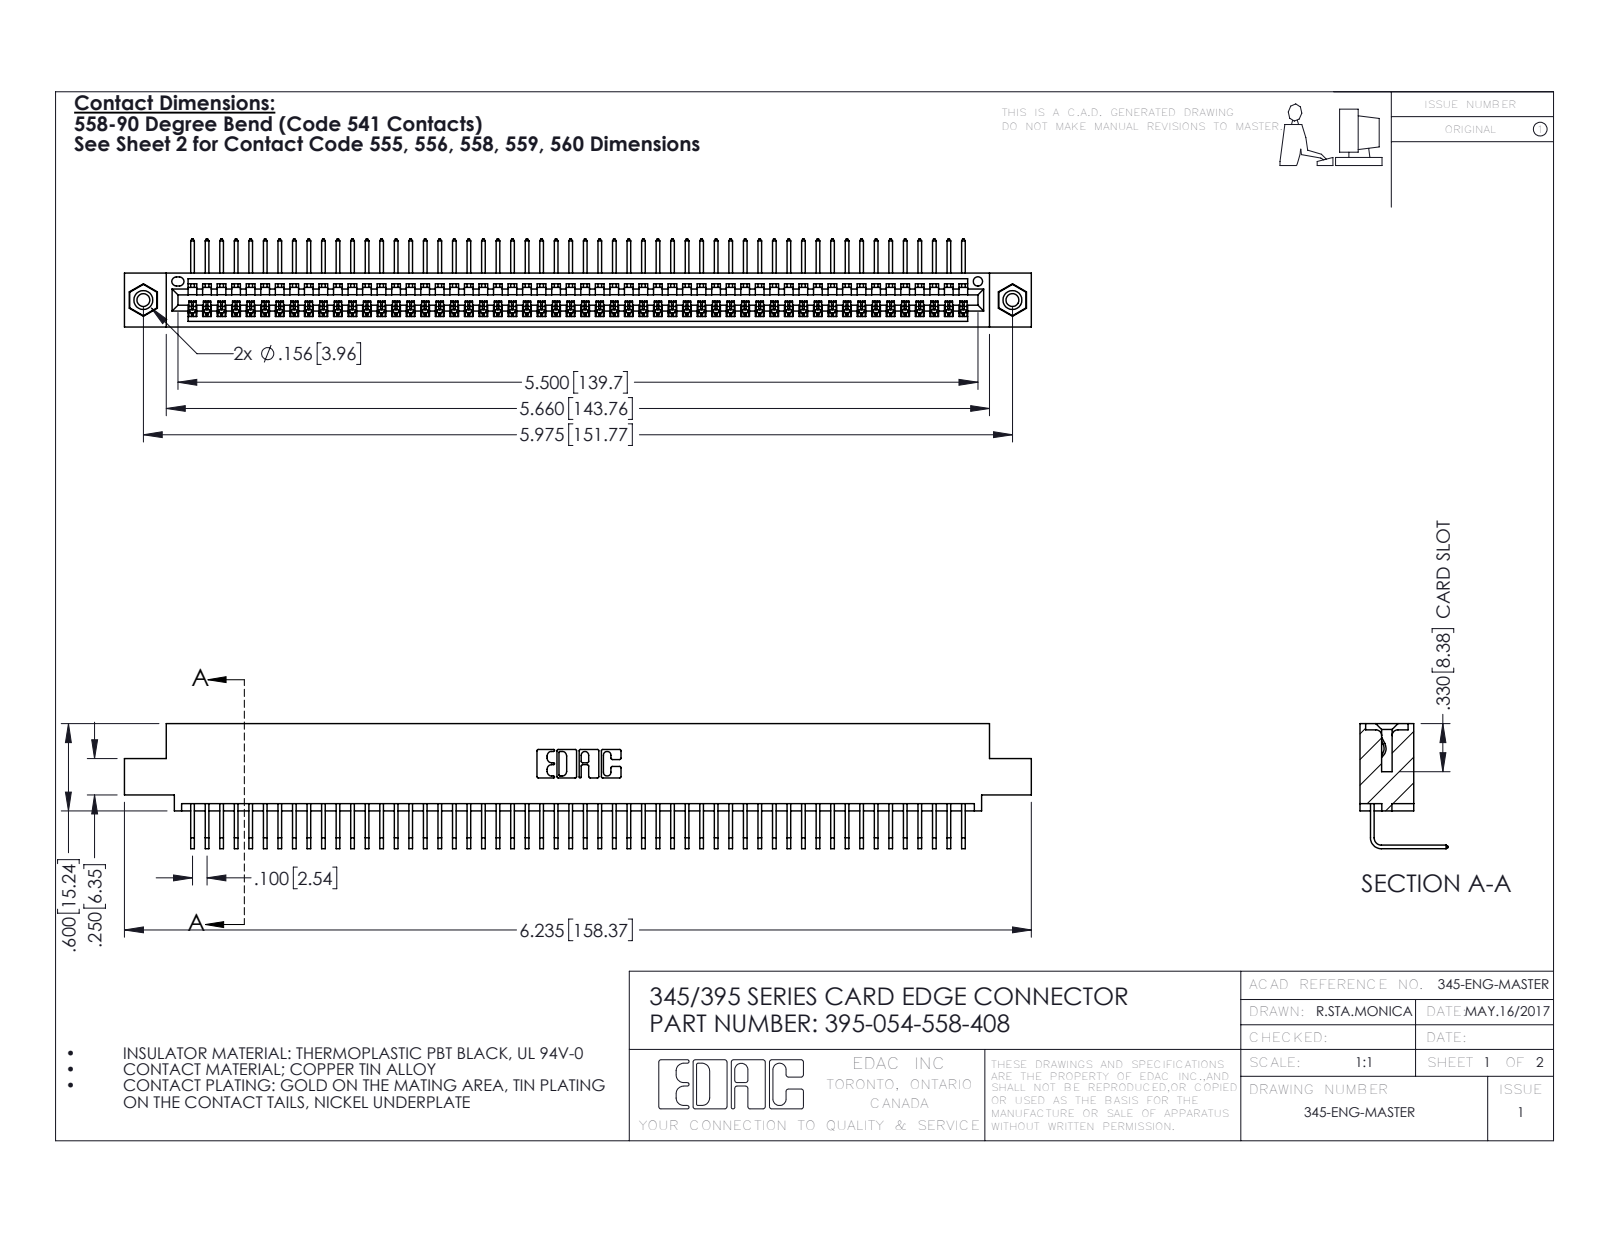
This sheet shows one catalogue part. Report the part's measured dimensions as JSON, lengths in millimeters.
{"part_name": "345-292-001_558 Tail - 2; 345 Part_0.110 Offset - 0.156 Dia-TI; 395-054-558-408; 345-250-001_345-250-003-102", "step_written_by": "SolidWorks 2016 (CONFIG_CONTROL_DESIGN)", "units": "millimeters", "bodies": {"solids": 57, "faces": 3430, "planar": 2384, "cylindrical": 1030, "other": 16}, "overall_size": [158.4, 21.8, 15.4], "volume_mm3": 15200, "surface_area_mm2": 21570, "round_holes": [[2.3, 2], [3.2, 2], [4, 2], [1.6, 1]], "round_bosses_or_shafts": [[3.9, 2]], "partial_cylinders_radius": [[0.2, 108], [0.3, 22], [0.2, 6], [0.8, 6], [0.7, 3], [0.8, 2], [1, 2], [0.4, 1]], "face_to_face_distances": [1.8, 7.6, 9.4, 5.1, 2.5, 6.9, 0.6, 5.7, 3.8, 1.8], "hole_center_spacings": [6.9, 145.8, 151.8]}
